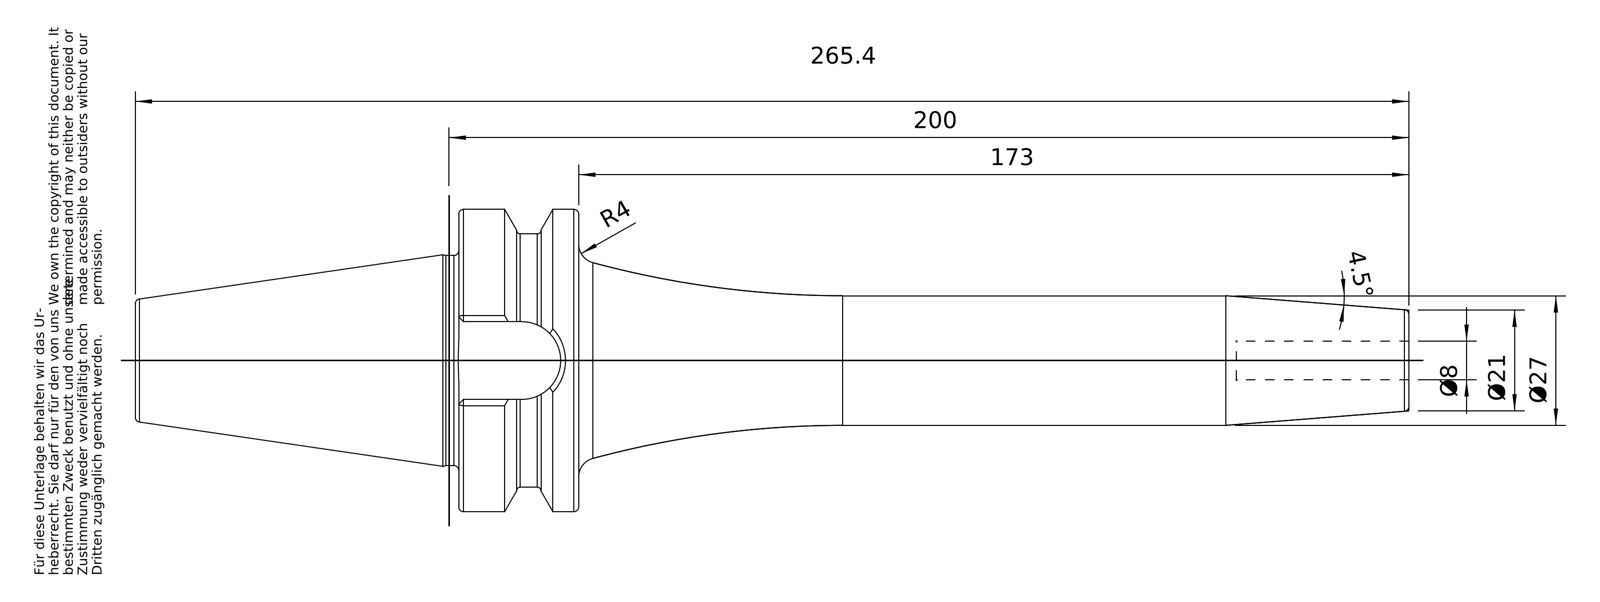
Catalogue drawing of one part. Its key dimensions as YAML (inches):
part_name: "40-646-08"
step_written_by: "PRO/ENGINEER BY PARAMETRIC TECHNOLOGY CORPORATION, 2010430 (CONFIG_CONTROL_DESIGN)"
units: inches
bodies: {solids: 1, faces: 98, planar: 26, cylindrical: 22, other: 50}
overall_size: [10.449, 2.48, 2.48]
volume: 14.22
surface_area: 57.07
round_holes:
  - {diameter: 0.315, count: 1}
  - {diameter: 0.545, count: 1}
  - {diameter: 0.67, count: 1}
  - {diameter: 0.689, count: 1}
round_bosses_or_shafts:
  - {diameter: 2.48, count: 1}
  - {diameter: 2.077, count: 1}
  - {diameter: 1.722, count: 1}
  - {diameter: 1.063, count: 1}
  - {diameter: 0.63, count: 1}
partial_cylinders:
  - {radius: 0.319, count: 1}
face_to_face_distances: [0.984, 1.768, 7.795, 6.811, 0.638, 2.654, 3.638, 10.449, 1.417, 9.031]
